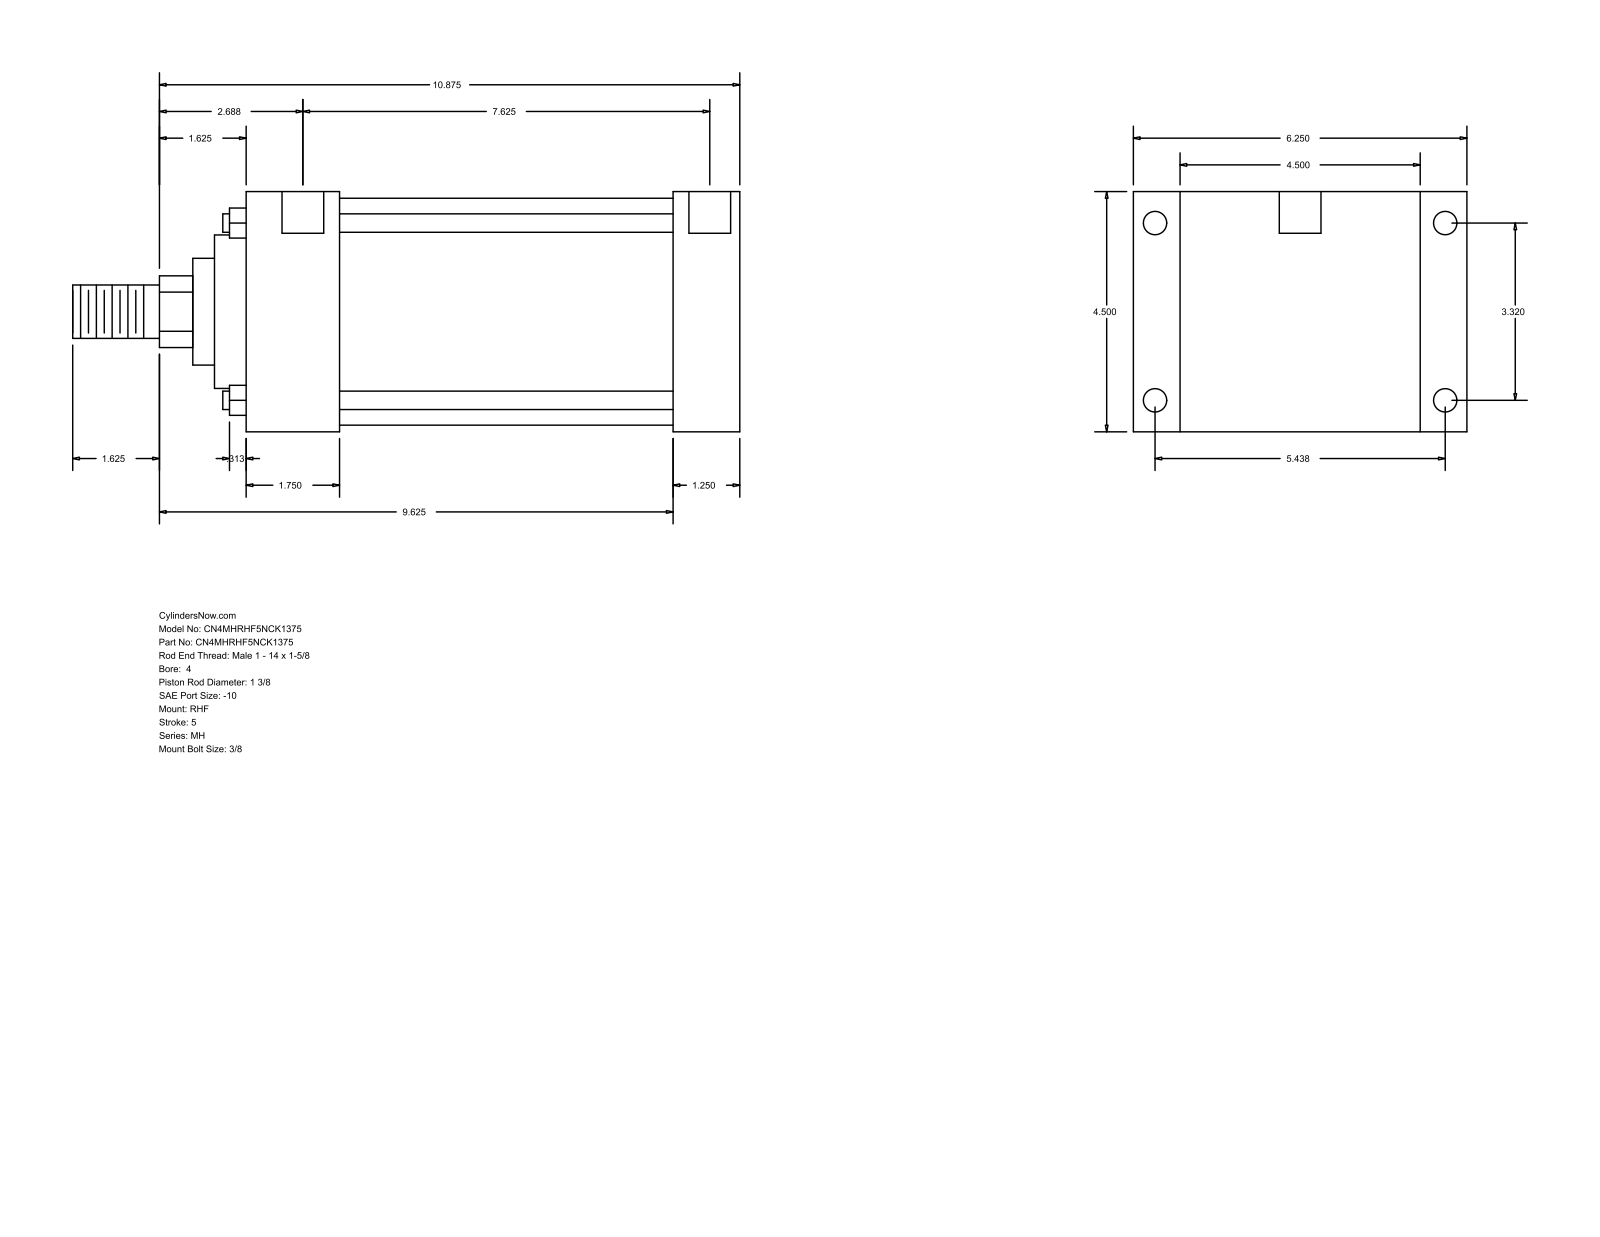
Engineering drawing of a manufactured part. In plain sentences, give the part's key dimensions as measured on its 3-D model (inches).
The part is named "MH_RHF__0400_1.375". Its 3-D file was written by "GSSL Pune (CONFIG_CONTROL_DESIGN)". It is 0 solids with 90 faces: 61 planar, 29 cylindrical and 0 other. Overall it measures 12.5 by 6.25 by 4.5 inches. Round holes: 4 of diameter 0.344, 4 of diameter 0.438, 2 of diameter 0.781. Round bosses or shafts: 4 of diameter 0.345, 1 of diameter 4.25, 1 of diameter 2.875, 1 of diameter 2, 1 of diameter 1.375, 1 of diameter 1. Partial cylindrical surfaces (rounded edges, fillets, slot ends): 1 of radius 0.672. The main face-to-face distances are 4.5, 1.25, 8, 9.25, 0.875, 5.375, 6.25, 1.75, 7.5, 6.25. The hole center spacings are 3.32, 5.438, 6.371, 7.75, 0.062, 0.063, 7.625, 7.687.
